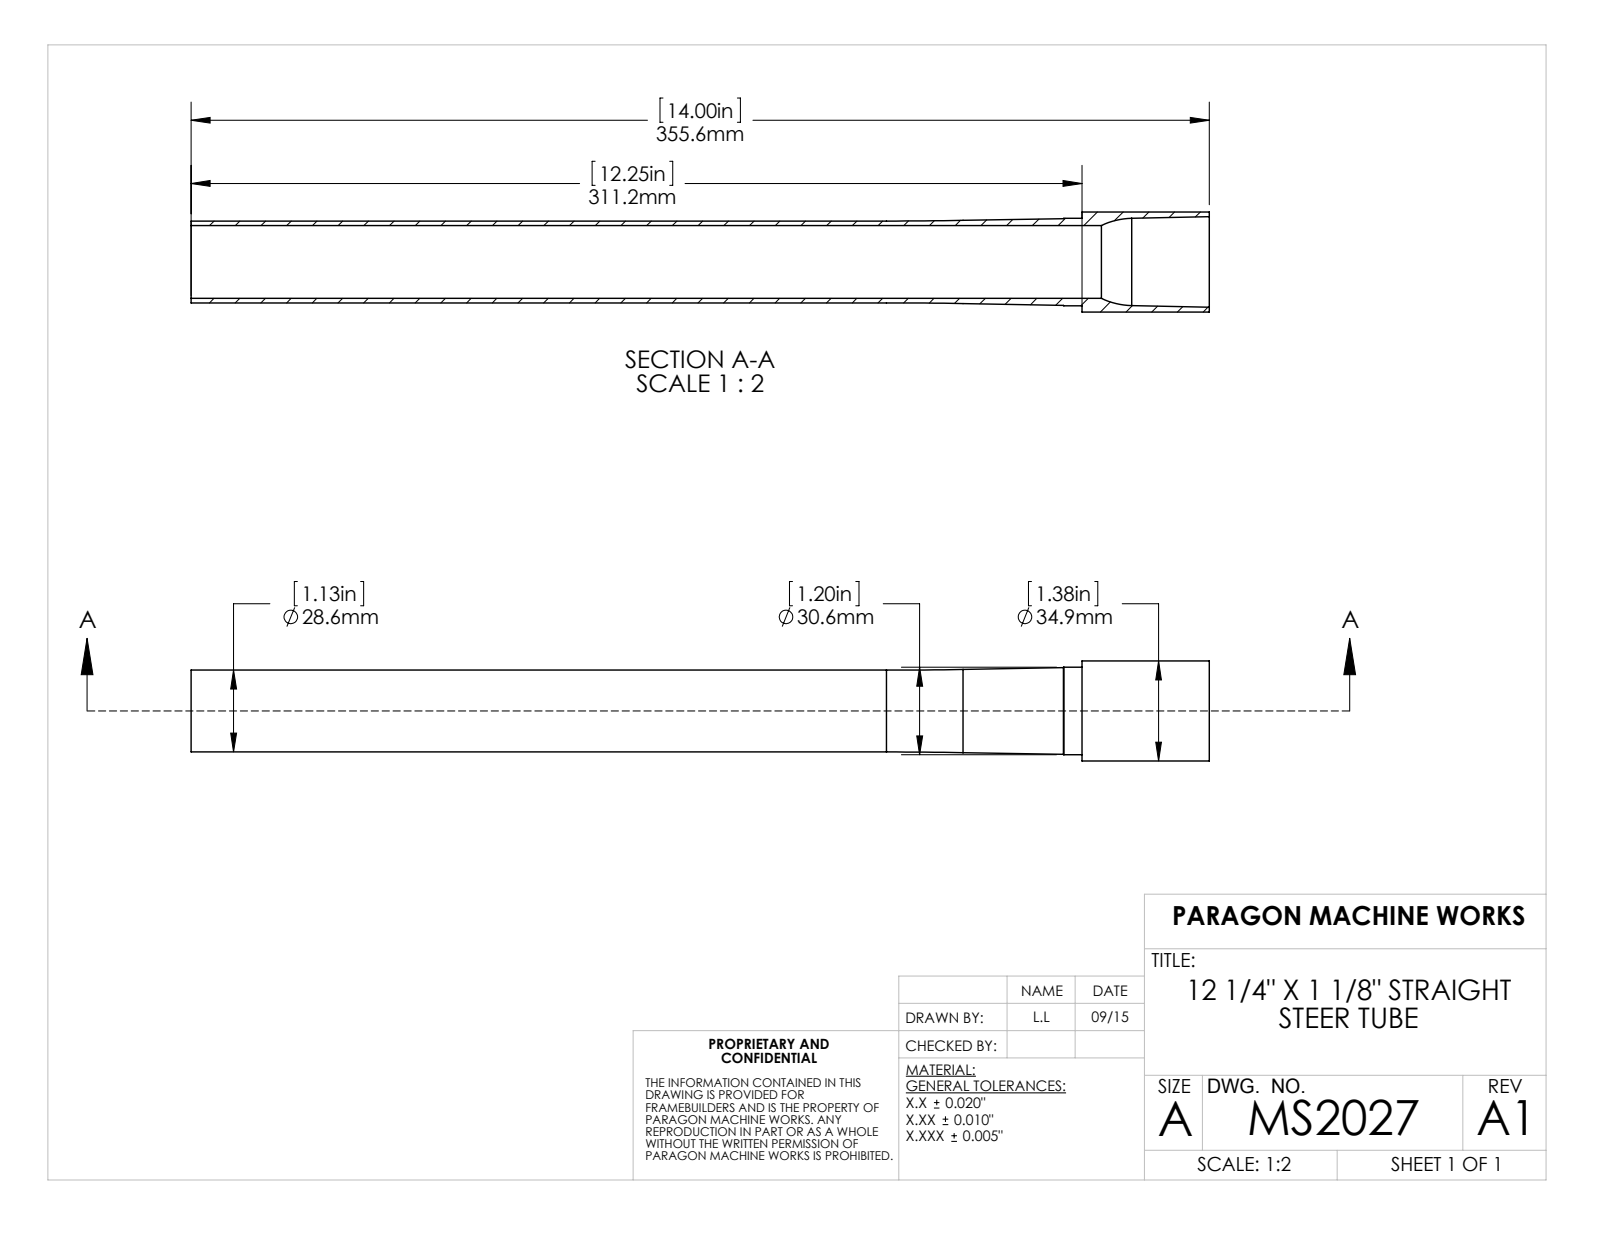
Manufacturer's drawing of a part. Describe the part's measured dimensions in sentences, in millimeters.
The part is named "MS2027". Its 3-D file was written by "SolidWorks 2015 (AUTOMOTIVE_DESIGN)". It is 1 solid with 21 faces: 3 planar, 8 cylindrical and 10 other. Overall it measures 355.6 by 34.9 by 34.9 millimeters. Its volume is 56 130 cubic millimeters and its surface area 62 520 square millimeters. Round holes: 1 of diameter 25.4. Round bosses or shafts: 1 of diameter 34.9, 1 of diameter 30.6, 1 of diameter 28.6. The main face-to-face distances are 44.5, 311.2, 355.6.
